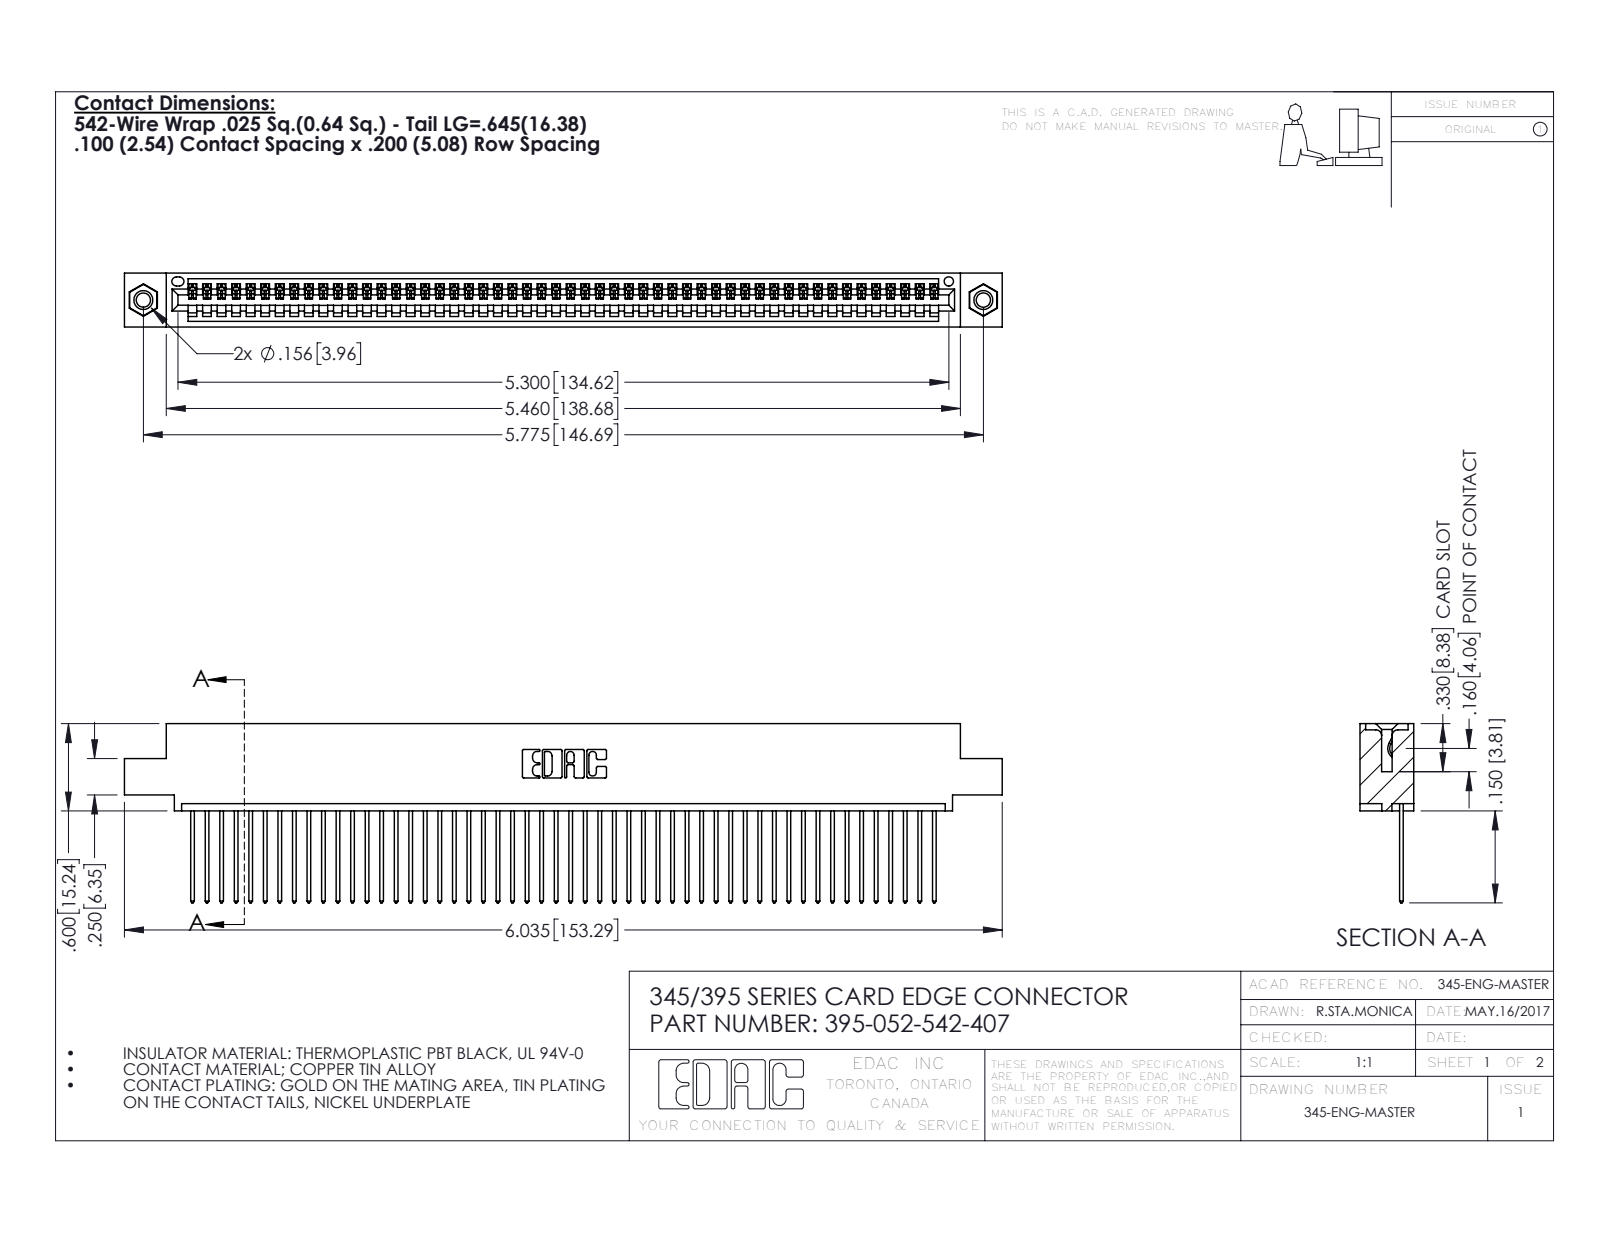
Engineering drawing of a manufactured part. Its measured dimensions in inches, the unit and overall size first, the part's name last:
Units: inches
Overall size (bounding box): 6.035 × 1.232 × 0.37
Round holes (diameter × count): ⌀0.098 ×2, ⌀0.125 ×2, ⌀0.156 ×2, ⌀0.064 ×1
Round bosses / shafts (diameter × count): ⌀0.155 ×2
Partial cylindrical surfaces — rounded edges, fillets, slot ends (radius × count): R0.006 ×104, R0.01 ×104, R0.01 ×22, R0.007 ×6, R0.031 ×6, R0.026 ×3, R0.031 ×2, R0.04 ×2
Main face-to-face distances: 0.072, 0.298, 0.098, 0.272, 0.025, 0.37, 0.2, 0.225, 0.149, 0.072
Hole centre spacings: 0.27, 5.539, 5.775
Volume: 0.895 in³ · Surface area: 31.74 in²
Bodies: 55 solids, 3206 faces (2196 planar, 994 cylindrical, 16 other)
Part name (STEP PRODUCT): 345-250-001_345-250-005-103; 345-292-001_345-293-142; 395-052-542-407; 345 Part_0.110 Offset - 0.156 Dia-TI
STEP written by: SolidWorks 2016 (CONFIG_CONTROL_DESIGN)
